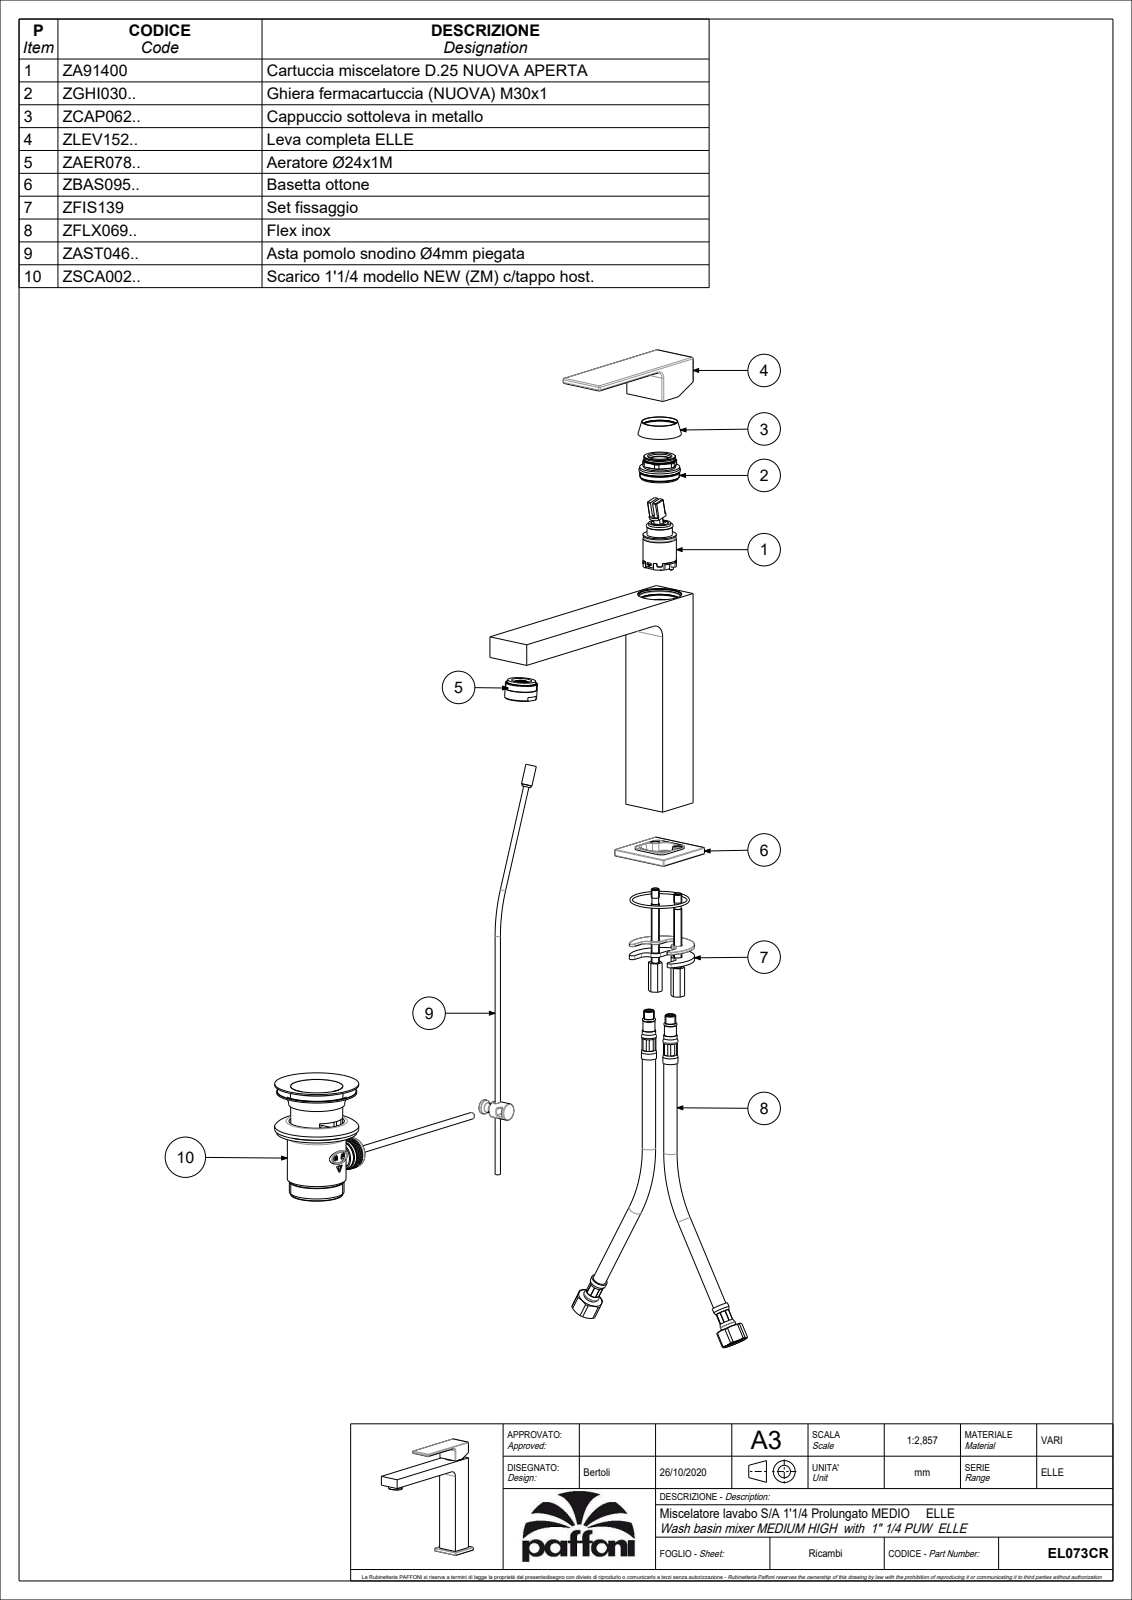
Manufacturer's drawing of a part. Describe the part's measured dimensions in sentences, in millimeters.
The part is named "EL073CR". Its 3-D file was written by "CREO PARAMETRIC BY PTC INC, 2020044 (CONFIG_CONTROL_DESIGN)". It is 2 solids with 160 faces: 57 planar, 61 cylindrical and 42 other. Overall it measures 208.6 by 196.28 by 48 millimeters. Its volume is 342 416 cubic millimeters and its surface area 63 109 square millimeters. Round holes: 1 of diameter 3, 1 of diameter 4.5, 1 of diameter 5.5, 1 of diameter 24.8, 1 of diameter 26.2, 1 of diameter 28. Round bosses or shafts: 1 of diameter 24, 1 of diameter 8, 1 of diameter 4. Partial cylindrical surfaces (rounded edges, fillets, slot ends): 13 of radius 1, 12 of radius 0.5, 8 of radius 1.5, 1 of radius 5, 1 of radius 10.5. The main face-to-face distances are 36, 35.5, 16, 44.78, 28.78, 40.78, 24.78, 4, 151.5, 167.5.
